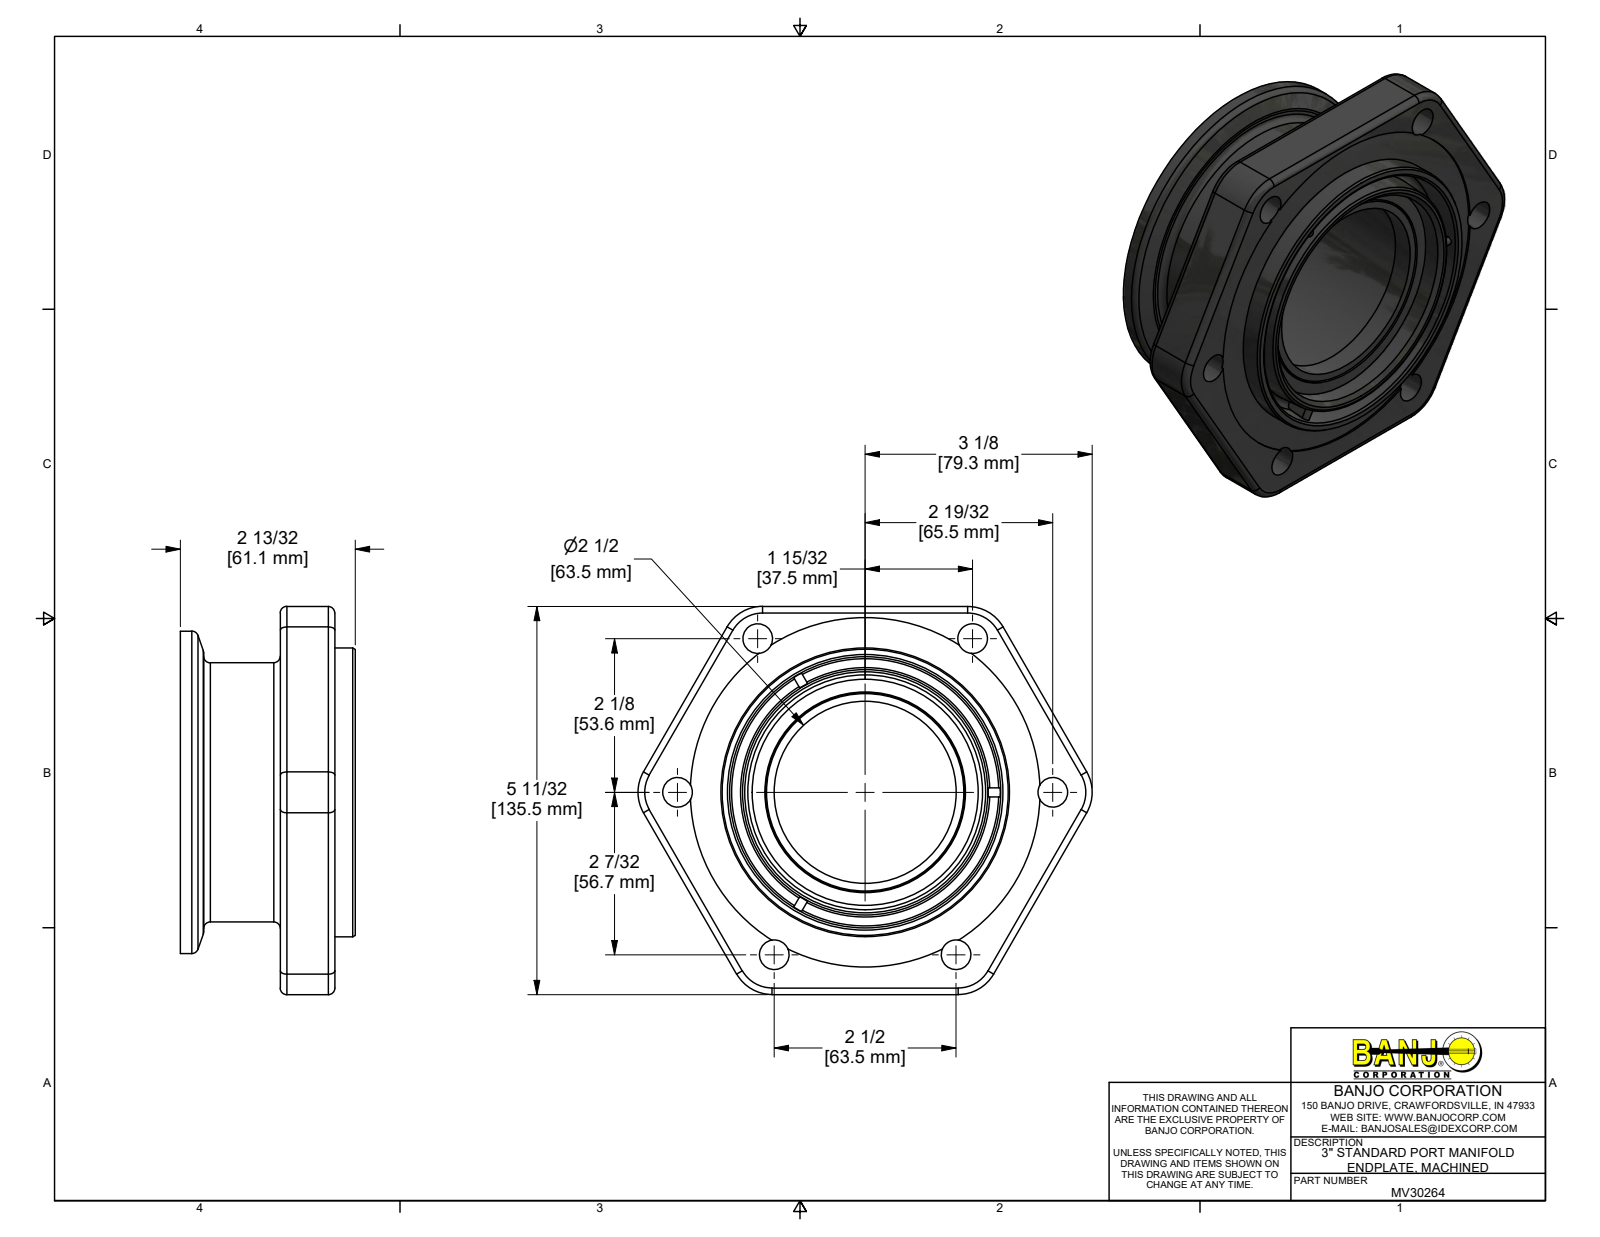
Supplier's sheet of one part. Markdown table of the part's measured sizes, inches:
| quantity | value |
| --- | --- |
| part name | MV30264; MV30264X |
| STEP written by | Autodesk Inventor 2019 (AUTOMOTIVE_DESIGN) |
| units | inches |
| bodies | 1 solid, 92 faces (23 planar, 40 cylindrical, 29 other) |
| overall size | 6.246 × 5.335 × 2.405 |
| volume | 19.75 in³ |
| surface area | 118.5 in² |
| round holes (diameter × count) | 0.406 × 6, 2.5 × 1, 3 × 1, 3.107 × 1, 3.74 × 1, 4.805 × 1 |
| round bosses / shafts (diameter × count) | 4.43 × 1, 3.97 × 1, 3.563 × 1 |
| partial cylindrical surfaces (radius × count) | 0.09 × 12, 0.562 × 6, 0.062 × 3 |
| main face-to-face distances | 0.725, 0.025, 0.75, 2.125, 2.1, 1.375, 2.025, 2, 1.275, 0.1 |
| hole center spacings | 2.382, 2.559, 2.578, 2.58, 2.599, 4.351, 4.433, 4.574 |
